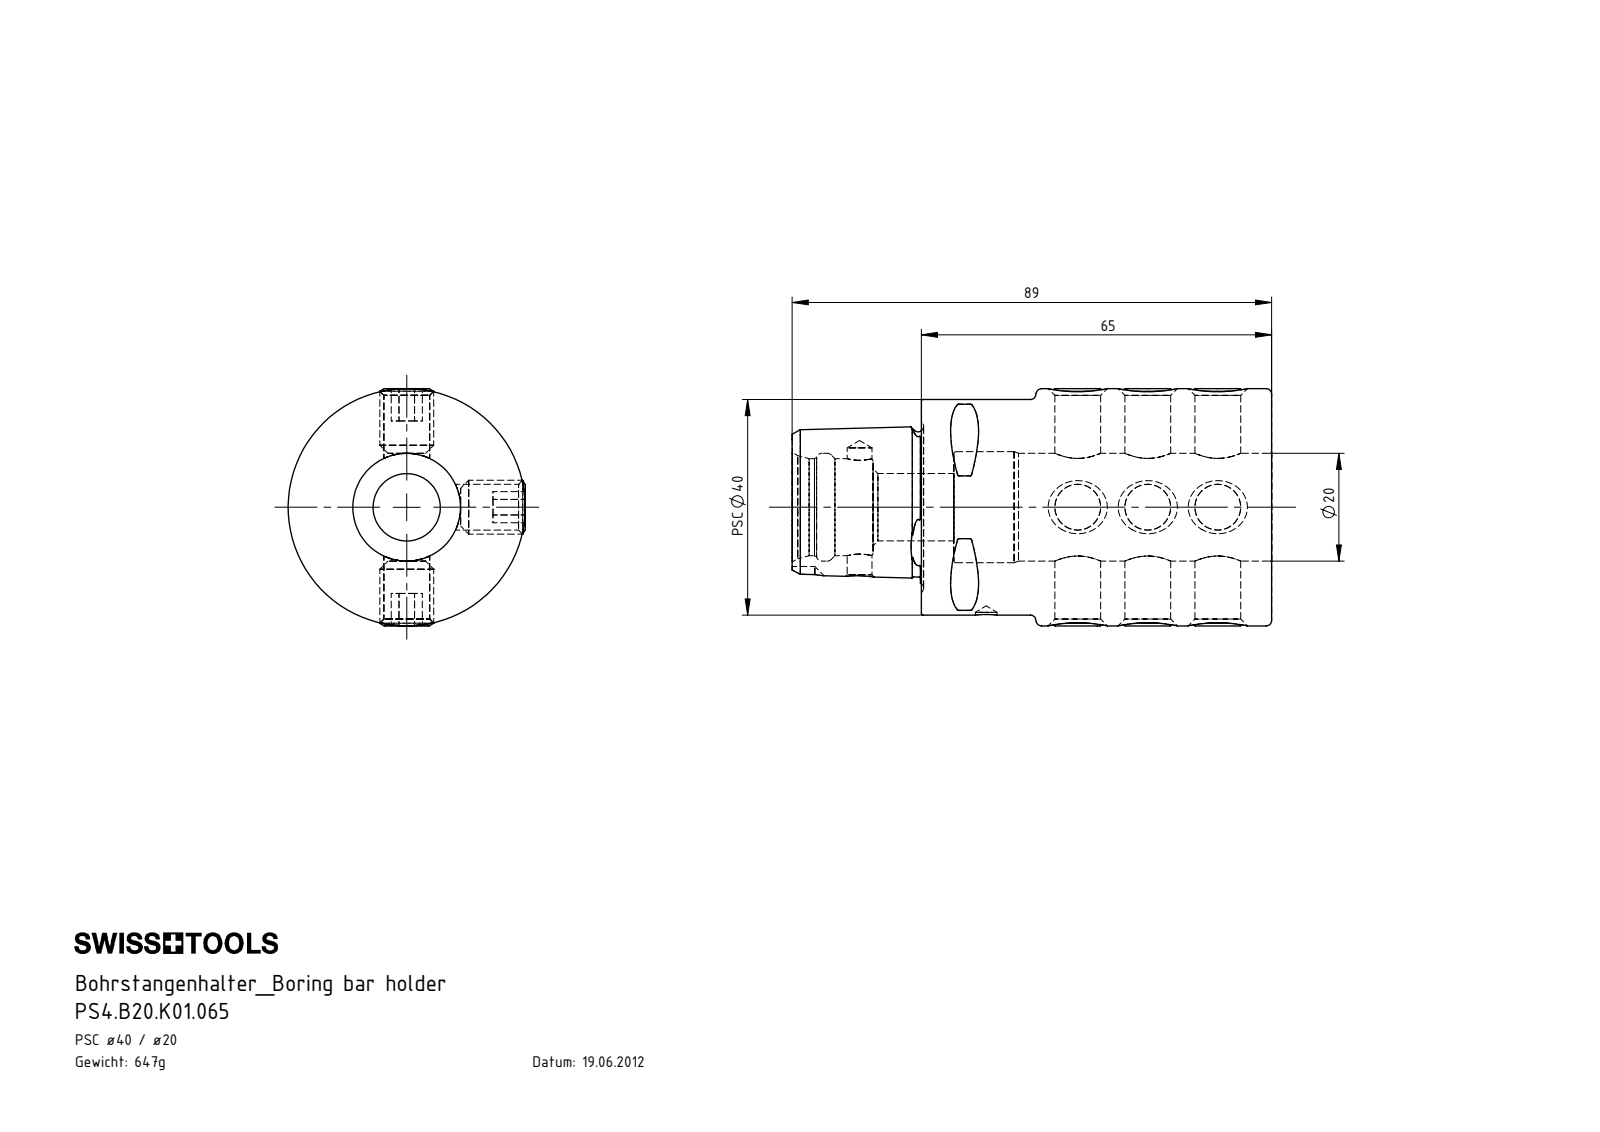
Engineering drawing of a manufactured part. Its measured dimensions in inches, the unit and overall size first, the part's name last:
Units: inches
Overall size (bounding box): 3.504 × 1.732 × 1.732
Round holes (diameter × count): ⌀0.335 ×6, ⌀0.157 ×1, ⌀0.181 ×1, ⌀0.492 ×1, ⌀0.709 ×1, ⌀0.787 ×1, ⌀0.811 ×1
Round bosses / shafts (diameter × count): ⌀0.394 ×6, ⌀1.732 ×1, ⌀1.575 ×1
Partial cylindrical surfaces — rounded edges, fillets, slot ends (radius × count): R0.012 ×8, R0.118 ×1
Main face-to-face distances: 0.236, 2.559, 0.197, 2.323, 0.256, 0.945, 1.181, 3.504, 1.26, 0.472
Hole centre spacings: 0.512, 1.024, 0.669, 0.925, 1.181, 1.594, 1.693, 2.106
Volume: 5.029 in³ · Surface area: 39.9 in²
Bodies: 10 solids, 332 faces (101 planar, 67 cylindrical, 164 other)
Part name (STEP PRODUCT): PS4.B20.K01.065; ISO 4026 - M10 x 12_PreviewCfg; PS4-B20.K01.065_A
STEP written by: SolidWorks 2017 (AUTOMOTIVE_DESIGN)
